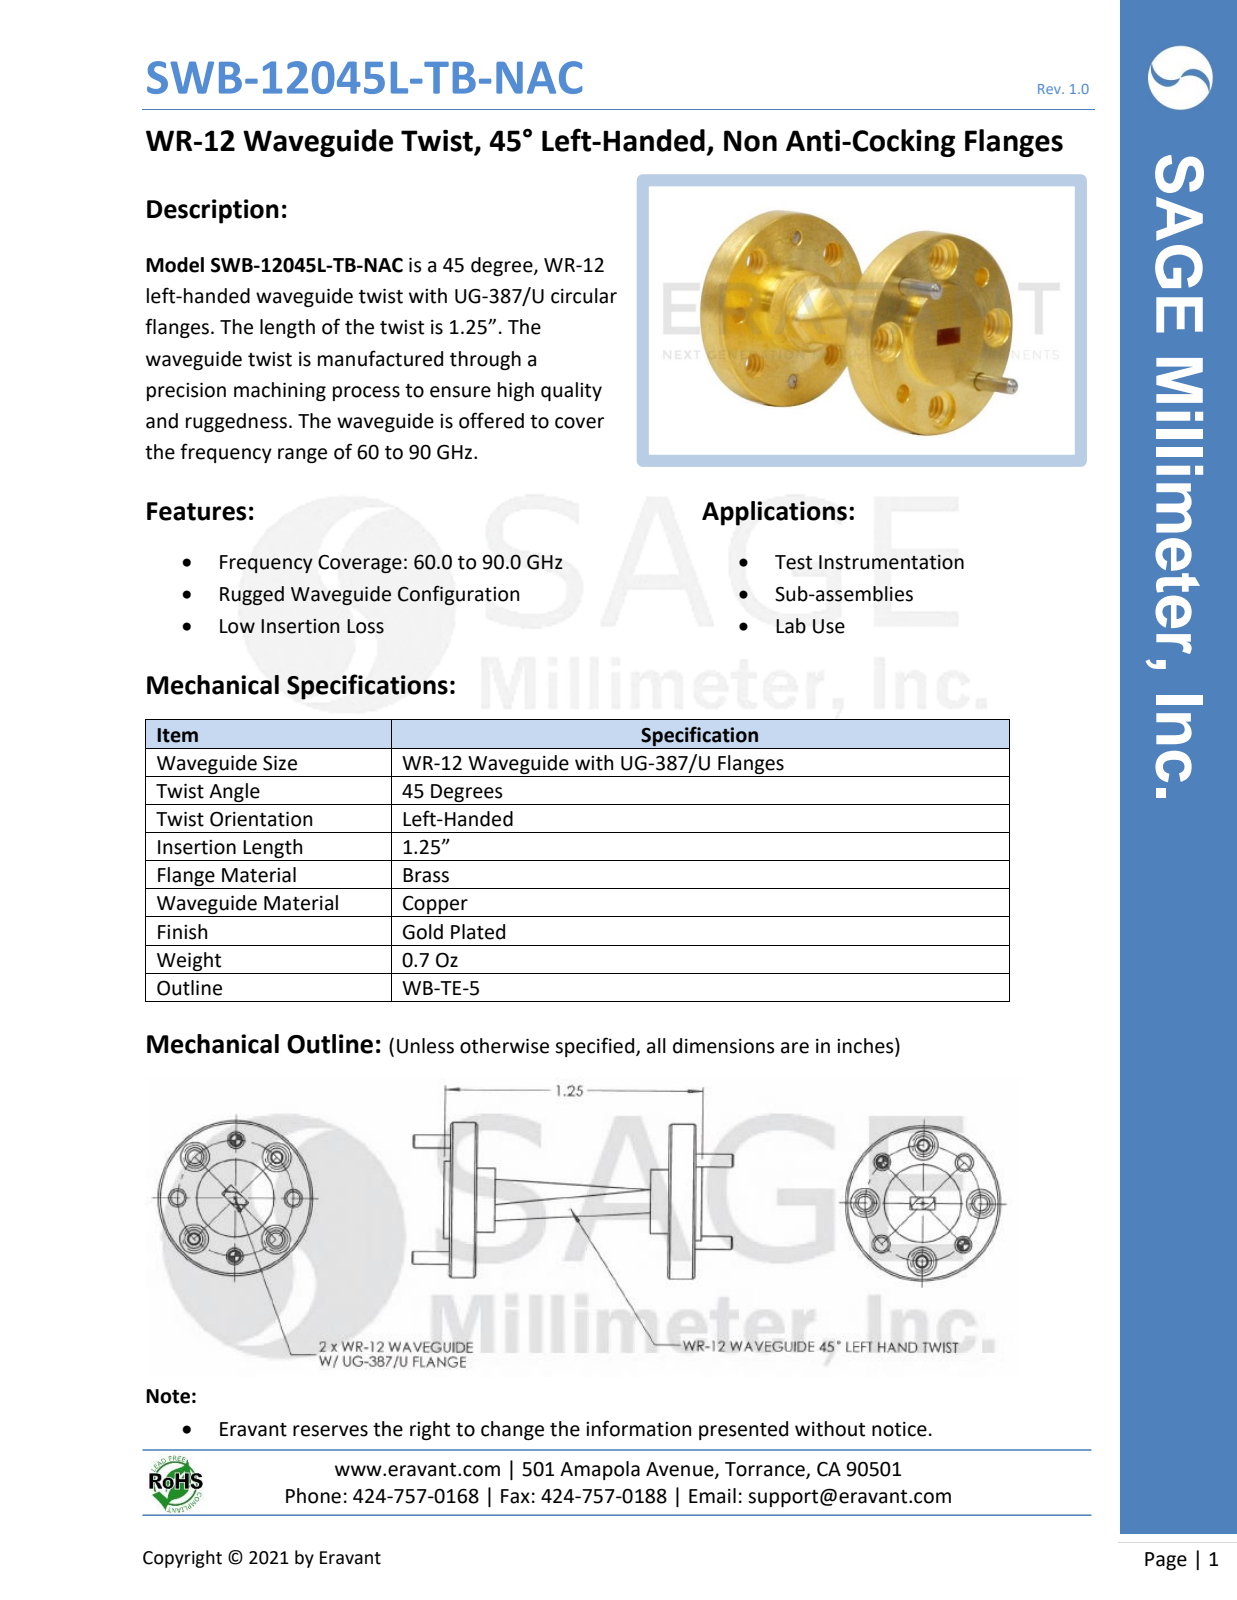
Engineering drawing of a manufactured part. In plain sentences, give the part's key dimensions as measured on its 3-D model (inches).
The part is named "SWB-12045L-TB". Its 3-D file was written by "SolidWorks 2016 (AUTOMOTIVE_DESIGN)". It is 5 solids with 146 faces: 34 planar, 68 cylindrical and 44 other. Overall it measures 1.555 by 0.75 by 0.75 inches. Its volume is 0.146 cubic inches and its surface area 3.637 square inches. Round holes: 8 of diameter 0.089, 8 of diameter 0.14, 4 of diameter 0.061, 4 of diameter 0.067. Round bosses or shafts: 4 of diameter 0.063, 1 of diameter 0.75, 1 of diameter 0.375, 1 of diameter 0.31. The main face-to-face distances are 0.13, 1.06, 0.93, 1.19, 0.03, 0.16, 1.09, 1.22, 1.25, 0.25. The hole center spacings are 0.215, 0.398, 0.519, 0.562.
